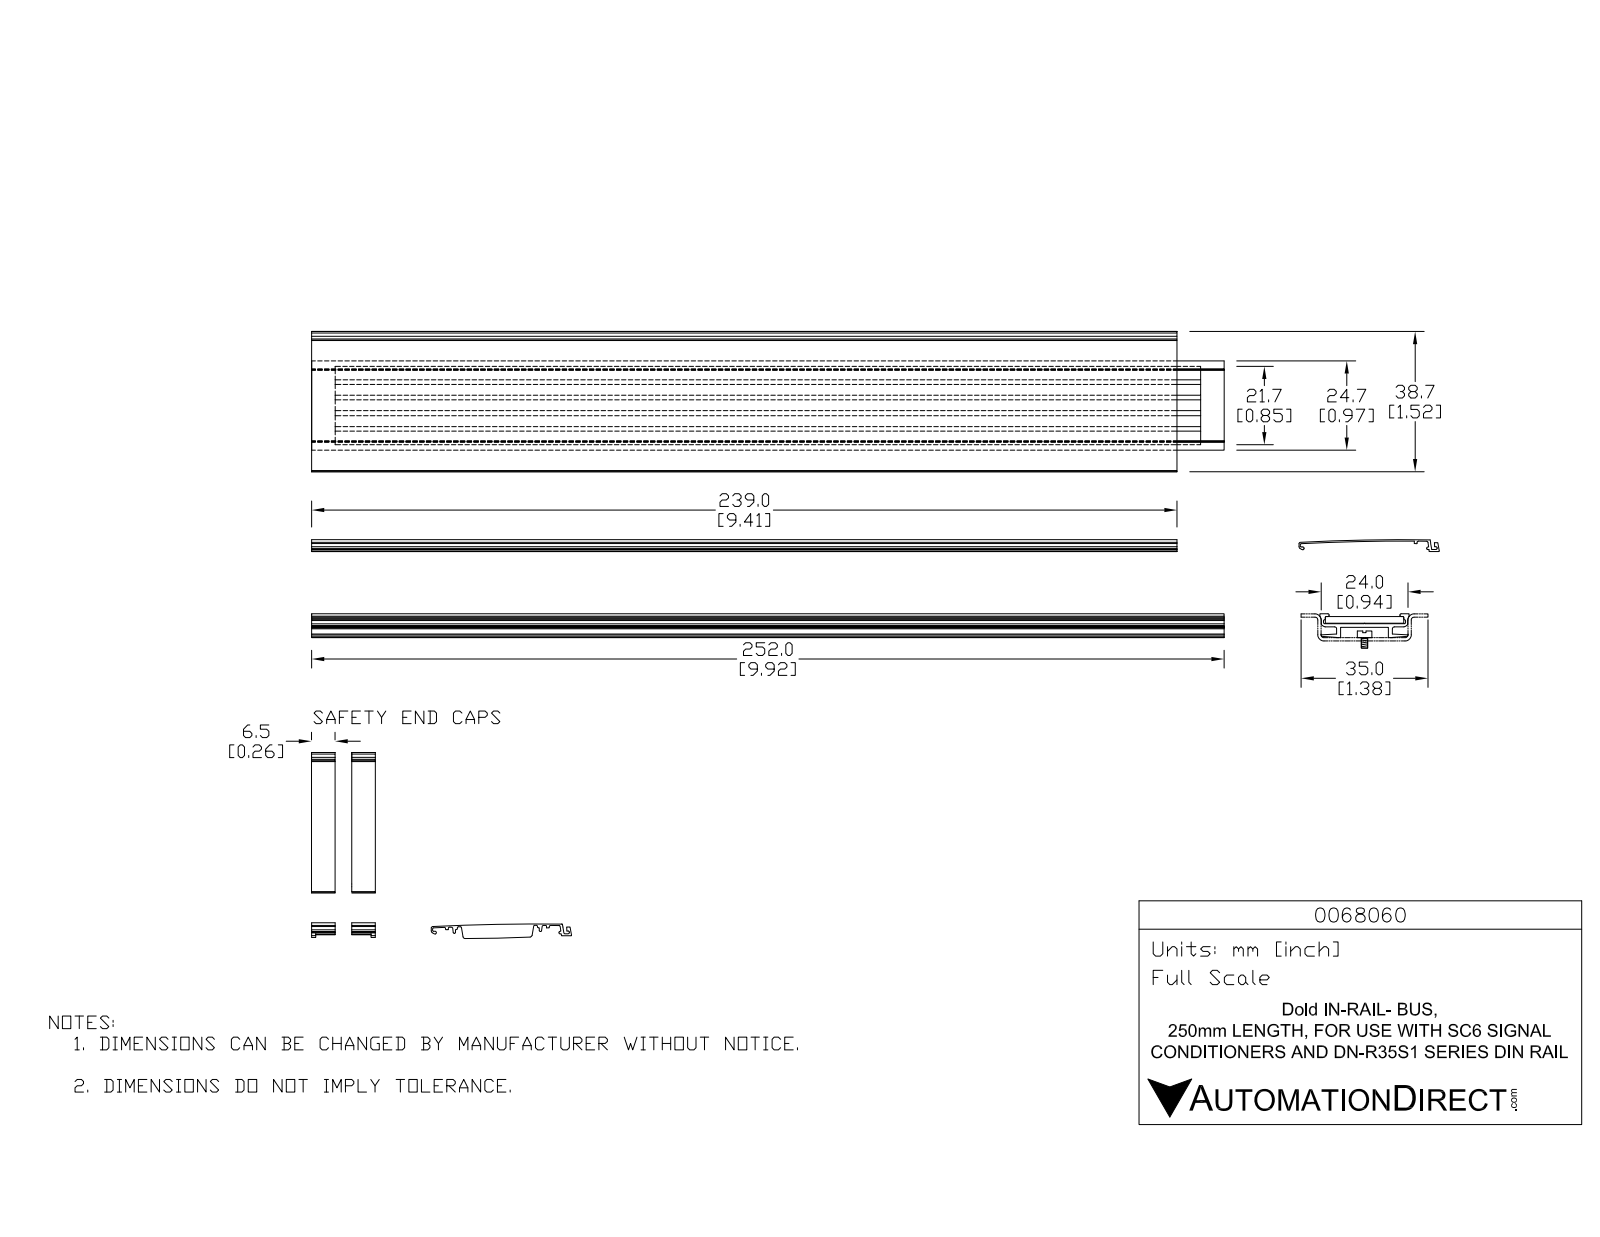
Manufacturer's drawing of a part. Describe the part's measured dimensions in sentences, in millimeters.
The part is named "POWER BUSS RAIL 250". Its 3-D file was written by "SolidWorks 2017 (AUTOMOTIVE_DESIGN)". It is 4 solids with 452 faces: 378 planar, 74 cylindrical and 0 other. Overall it measures 407.5 by 38.73 by 17.44 millimeters. Its volume is 24 408 cubic millimeters and its surface area 58 493 square millimeters. Partial cylindrical surfaces (rounded edges, fillets, slot ends): 14 of radius 0.25, 3 of radius 0.51, 3 of radius 0.73, 3 of radius 547.43, 2 of radius 0.71, 1 of radius 0.15, 1 of radius 0.16, 1 of radius 0.26. The main face-to-face distances are 1.84, 1.69, 0.99, 1.14, 2.83, 2.71, 1.72, 1.57, 3.62, 0.87.
